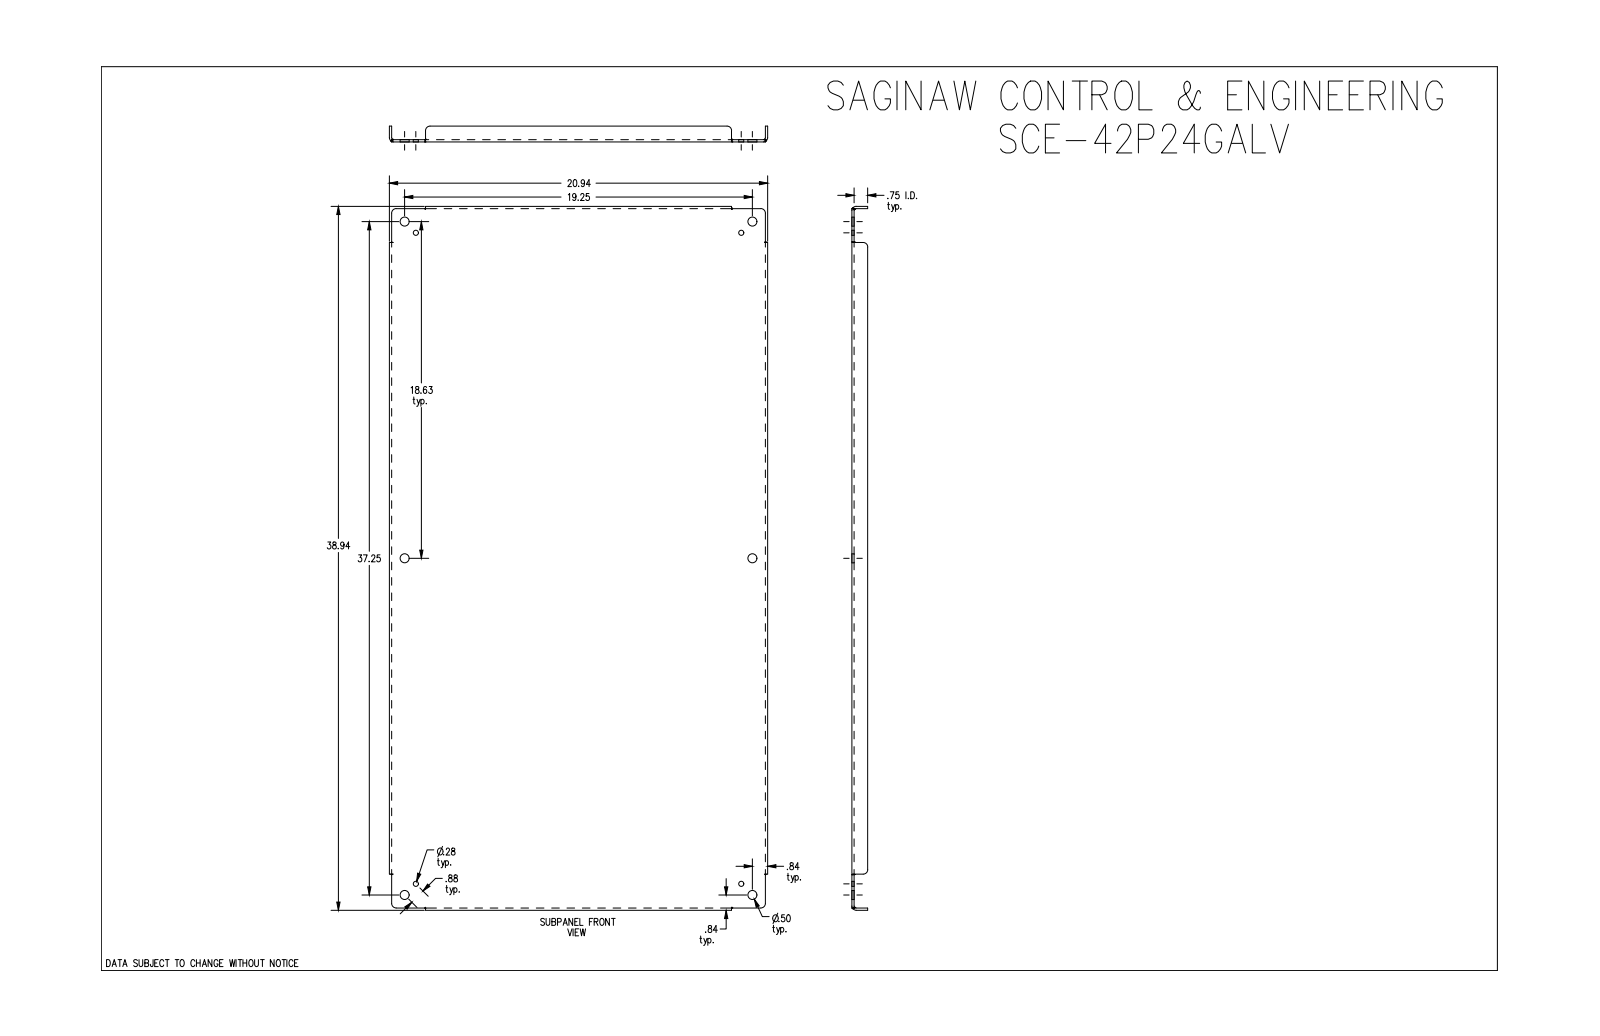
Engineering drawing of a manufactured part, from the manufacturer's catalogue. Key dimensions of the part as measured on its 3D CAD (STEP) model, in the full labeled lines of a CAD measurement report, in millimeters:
Part name (STEP PRODUCT): SCE-42P24GALV
STEP written by: SolidWorks 2019 (CONFIG_CONTROL_DESIGN)
Units: millimetres
Bodies: 1 solid, 84 faces (30 planar, 30 cylindrical, 24 other)
Overall size (bounding box): 989 × 531.8 × 22.2
Volume: 1 806 000 mm³ · Surface area: 1 149 000 mm²
Round holes (diameter × count): ⌀12.7 ×6, ⌀7.1 ×4
Partial cylindrical surfaces — rounded edges, fillets, slot ends (radius × count): R6.4 ×8, R2.8 ×4, R6 ×4
Main face-to-face distances: 3.2, 3.2, 528.7, 525.4, 531.8, 985.9, 19.1, 22.2, 982.6, 989
Hole centre spacings: 22.2, 457.6, 473.1, 473.5, 658.1, 680.3, 930.6, 1043.9
